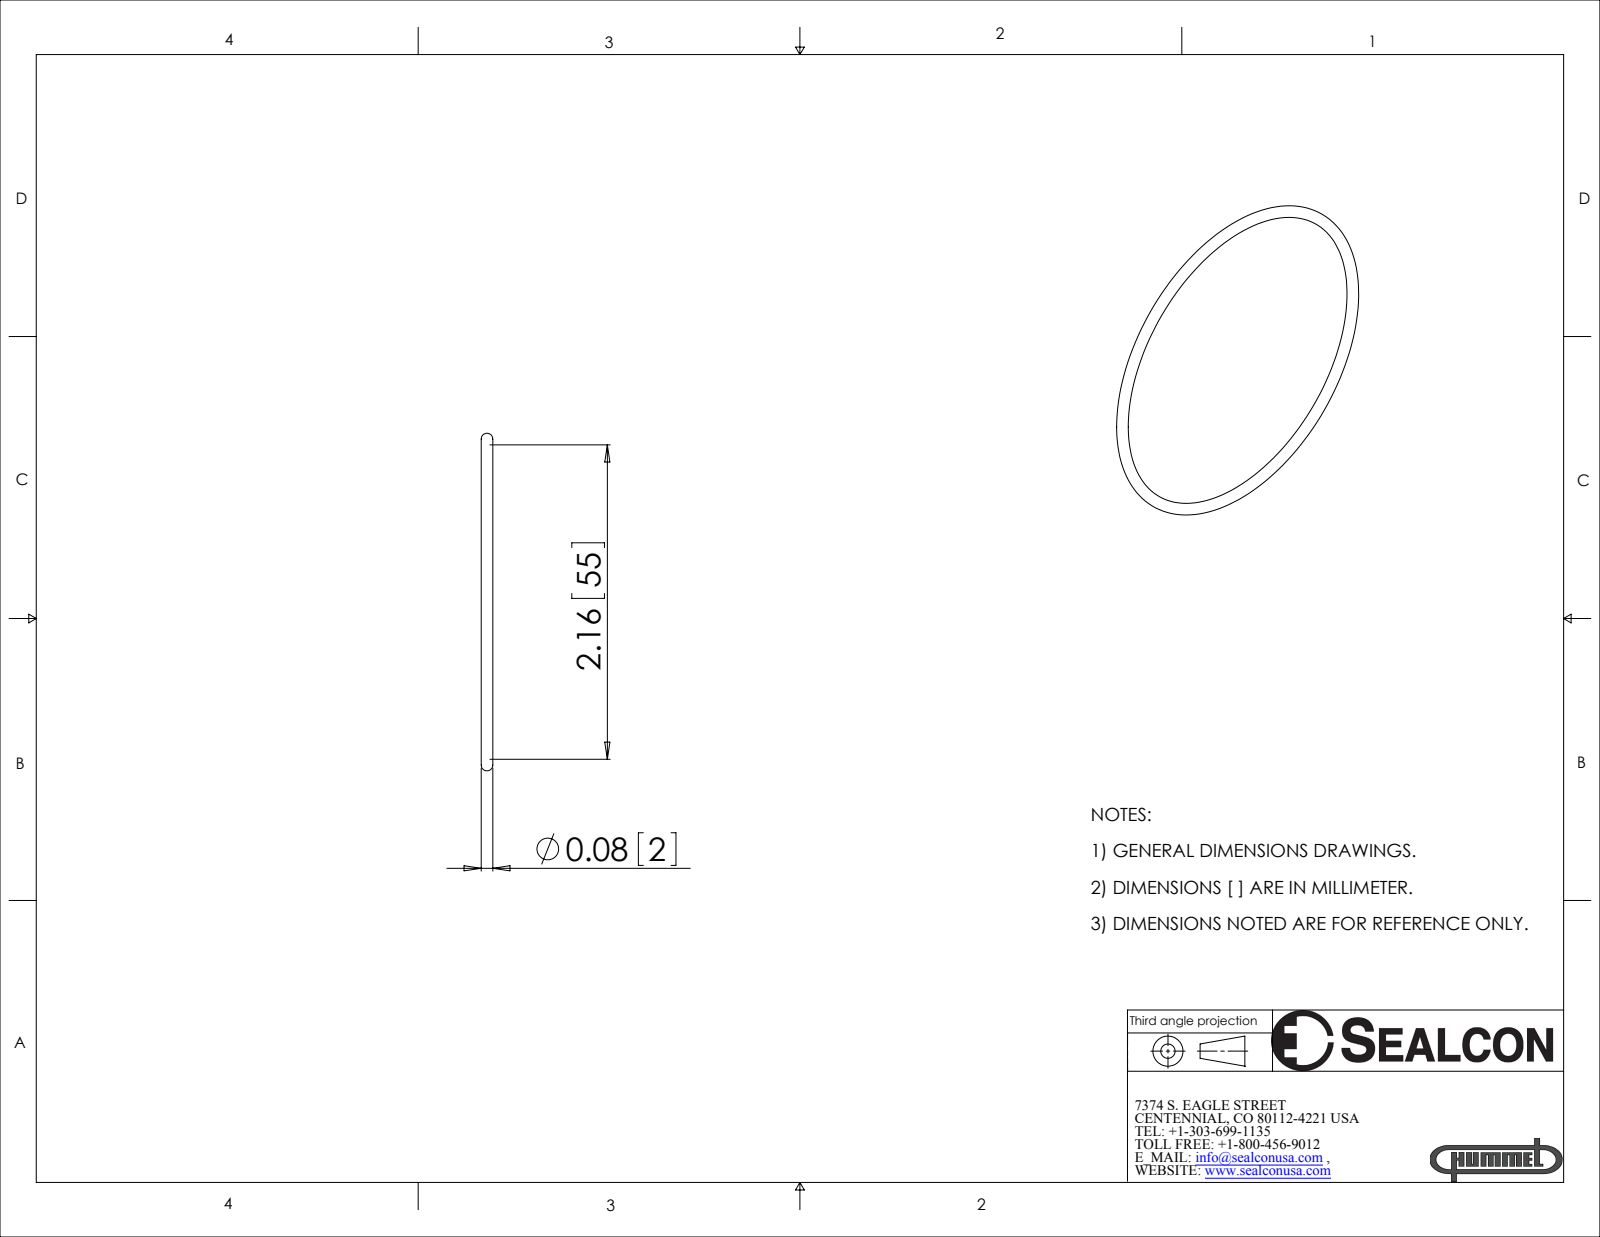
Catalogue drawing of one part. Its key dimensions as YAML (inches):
part_name: "OM-63-SI"
step_written_by: "SolidWorks 2008 (CONFIG_CONTROL_DESIGN)"
units: inches
bodies: {solids: 1, faces: 4, planar: 0, cylindrical: 0, other: 4}
overall_size: [2.32, 2.32, 0.08]
volume: 0.035
surface_area: 1.769
